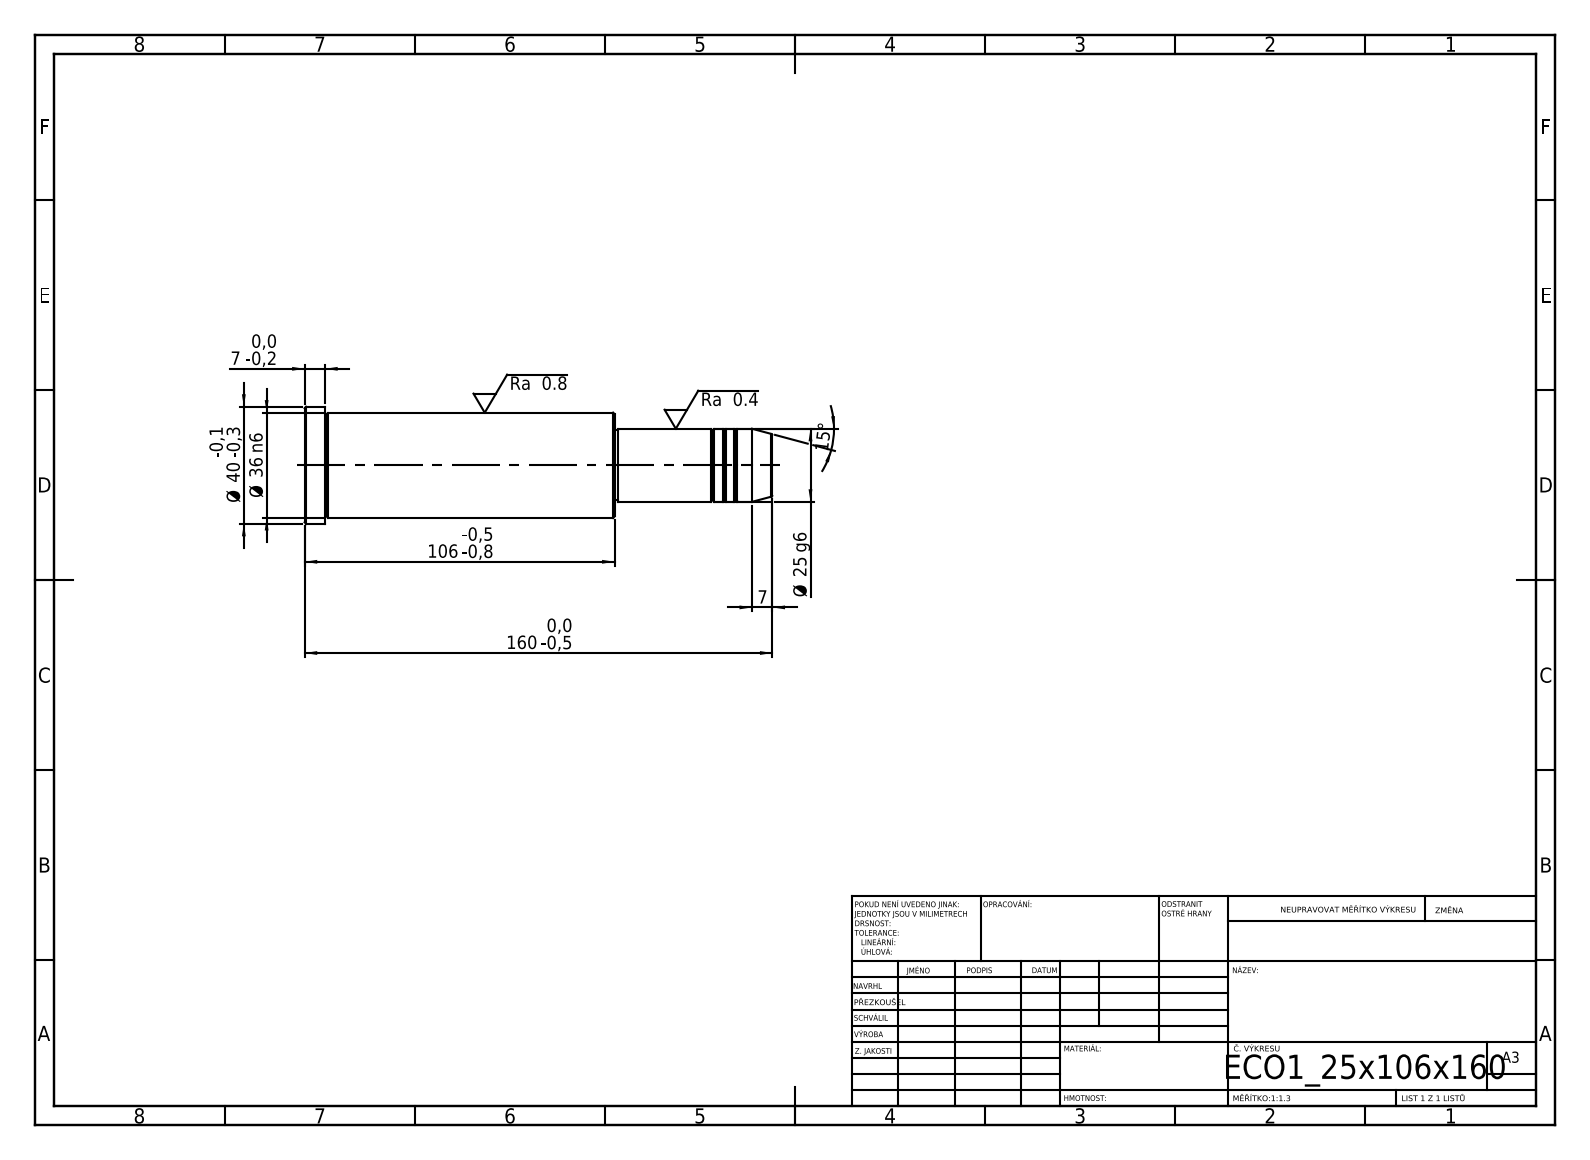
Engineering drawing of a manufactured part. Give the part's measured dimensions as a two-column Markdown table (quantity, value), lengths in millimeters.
| quantity | value |
| --- | --- |
| STEP written by | SolidWorks 2019 (CONFIG_CONTROL_DESIGN) |
| units | millimeters |
| bodies | 1 solid, 43 faces (5 planar, 14 cylindrical, 24 other) |
| overall size | 160 × 40 × 40 |
| volume | 135 379 mm³ |
| surface area | 18 853 mm² |
| round bosses / shafts (diameter × count) | 40 × 1, 36 × 1, 25 × 1, 24 × 1 |
| main face-to-face distances | 106, 54, 160, 153, 99, 7, 53, 1, 100, 107 |
